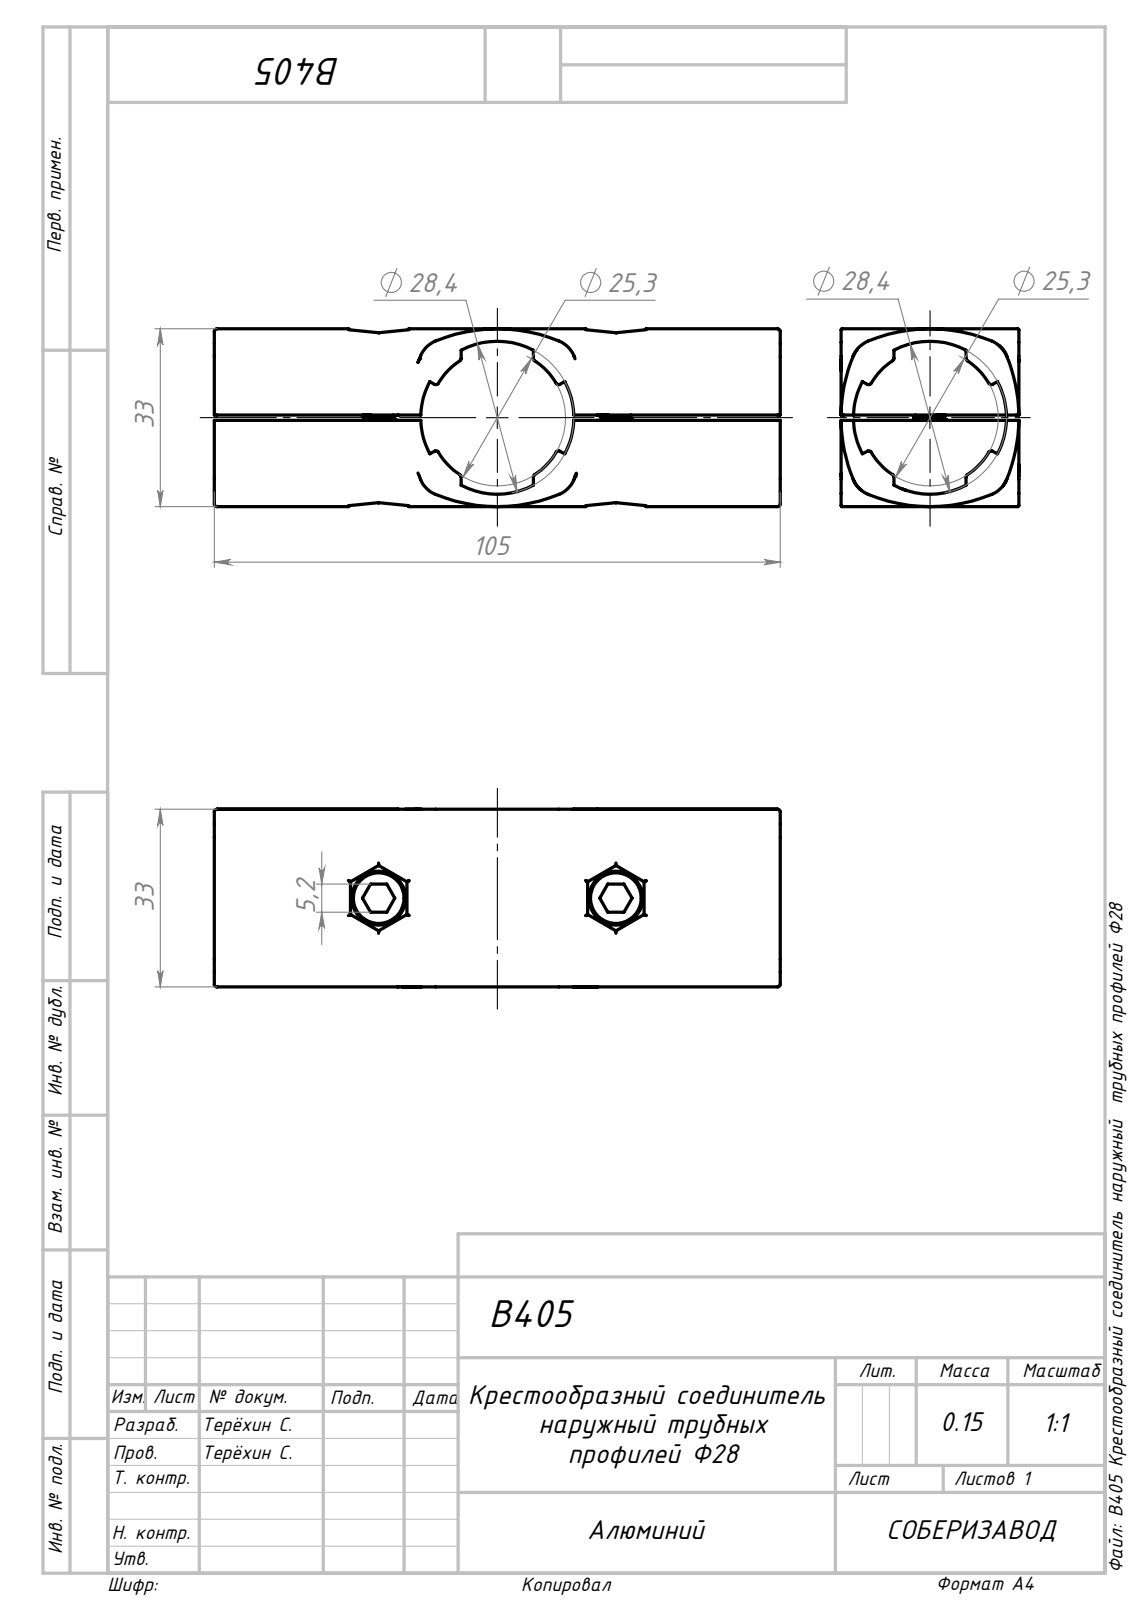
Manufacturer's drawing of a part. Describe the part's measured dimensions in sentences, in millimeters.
The part is named "B405 Крестообразный соединитель наружный трубных профилей Ф28". Its 3-D file was written by "SolidWorks 2022 (AUTOMOTIVE_DESIGN)". It is 6 solids with 664 faces: 200 planar, 254 cylindrical and 210 other. Overall it measures 105 by 33 by 32.99 millimeters. Its volume is 49 273 cubic millimeters and its surface area 28 025 square millimeters. Round holes: 2 of diameter 5.2, 2 of diameter 6.5, 1 of diameter 28.4. Round bosses or shafts: 2 of diameter 10, 2 of diameter 6. Partial cylindrical surfaces (rounded edges, fillets, slot ends): 32 of radius 1, 20 of radius 0.5, 8 of radius 5, 8 of radius 30, 2 of radius 12.65, 1 of radius 14.2. The main face-to-face distances are 1, 6, 7, 10.28, 22, 13, 23, 82, 59, 33. The hole center spacings are 44.
